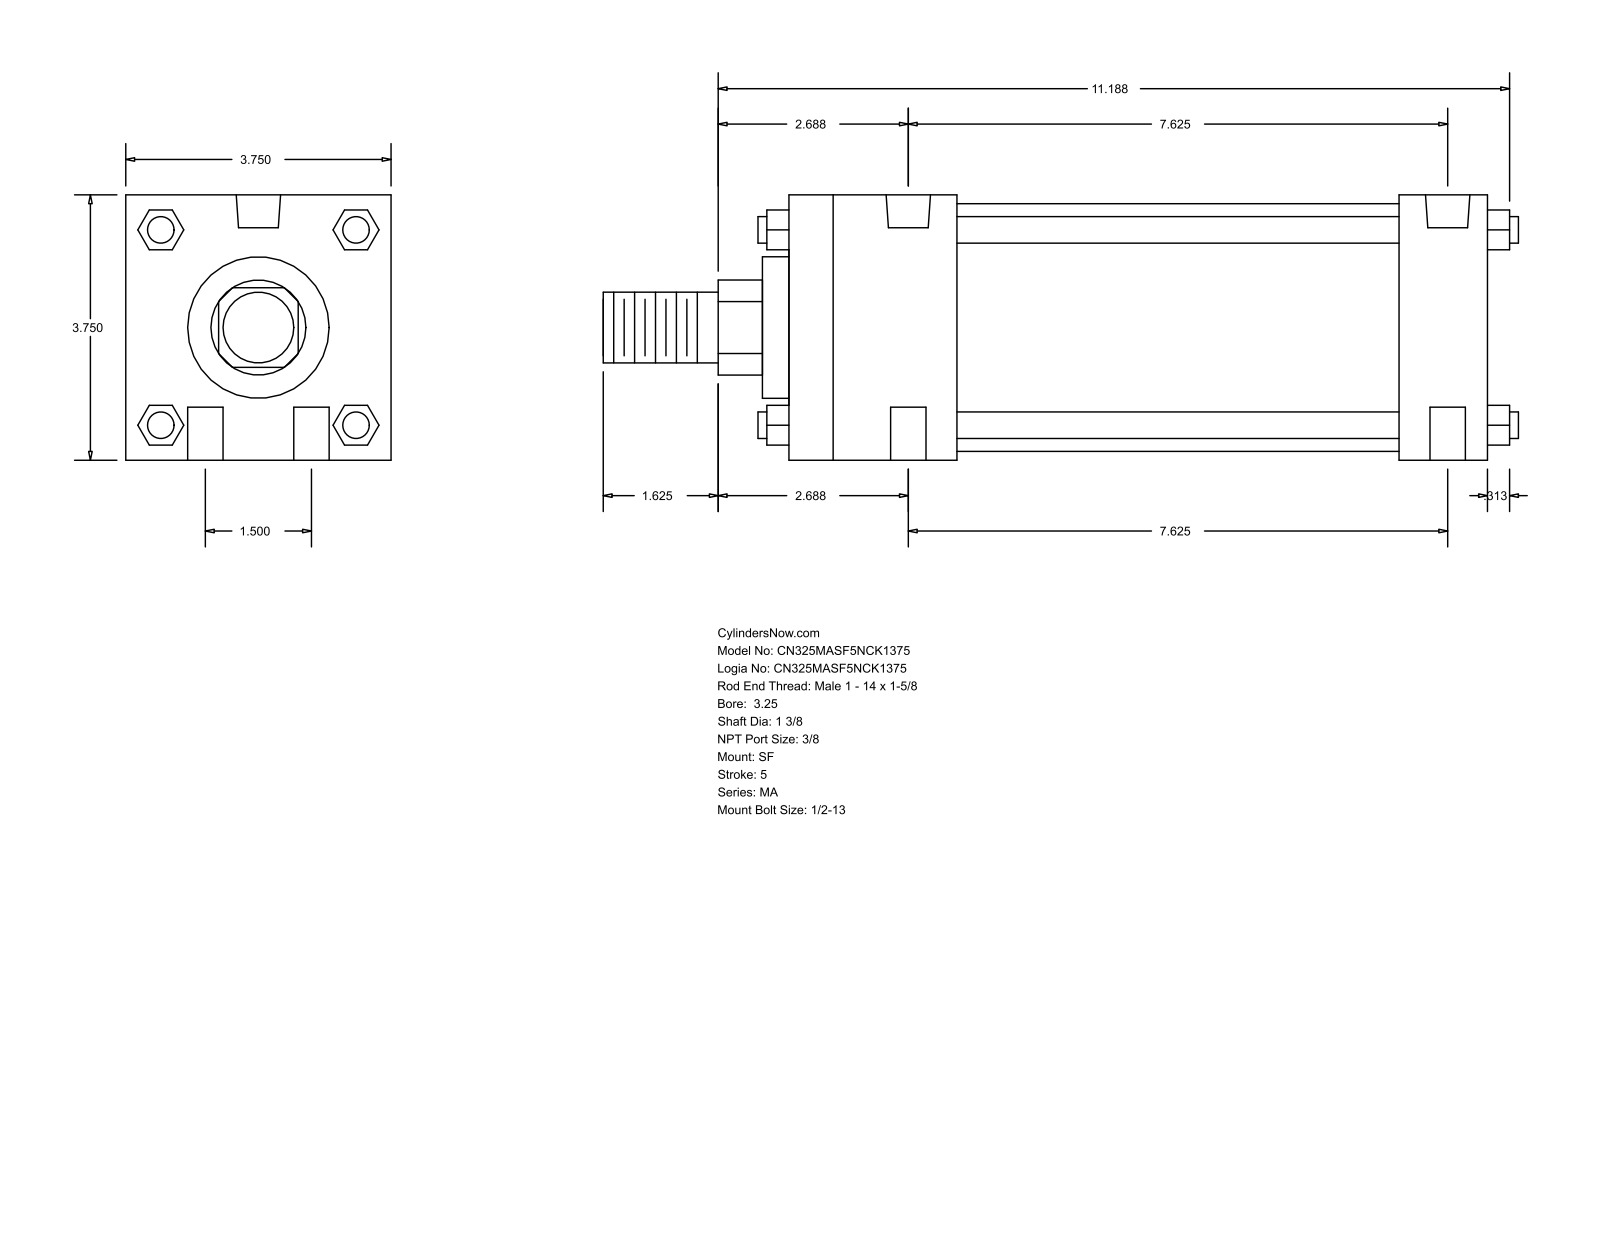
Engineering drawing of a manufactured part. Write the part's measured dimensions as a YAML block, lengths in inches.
part_name: "MA_SF__0325_1.375"
step_written_by: "GSSL Pune (CONFIG_CONTROL_DESIGN)"
units: inches
bodies: {solids: 0, faces: 124, planar: 94, cylindrical: 30, other: 0}
overall_size: [12.937, 3.75, 3.75]
round_holes:
  - {diameter: 0.5, count: 4}
  - {diameter: 0.437, count: 2}
  - {diameter: 0.627, count: 2}
round_bosses_or_shafts:
  - {diameter: 0.375, count: 4}
  - {diameter: 3.5, count: 1}
  - {diameter: 2, count: 1}
  - {diameter: 1.375, count: 1}
  - {diameter: 1, count: 1}
partial_cylinders:
  - {radius: 0.672, count: 1}
face_to_face_distances: [3.75, 9.875, 8.625, 1.25, 2.375, 6.25, 7.5, 0.375, 2.75, 9]
hole_center_spacings: [0.75, 7.662, 7.625, 1.5, 7.771, 7.25]
